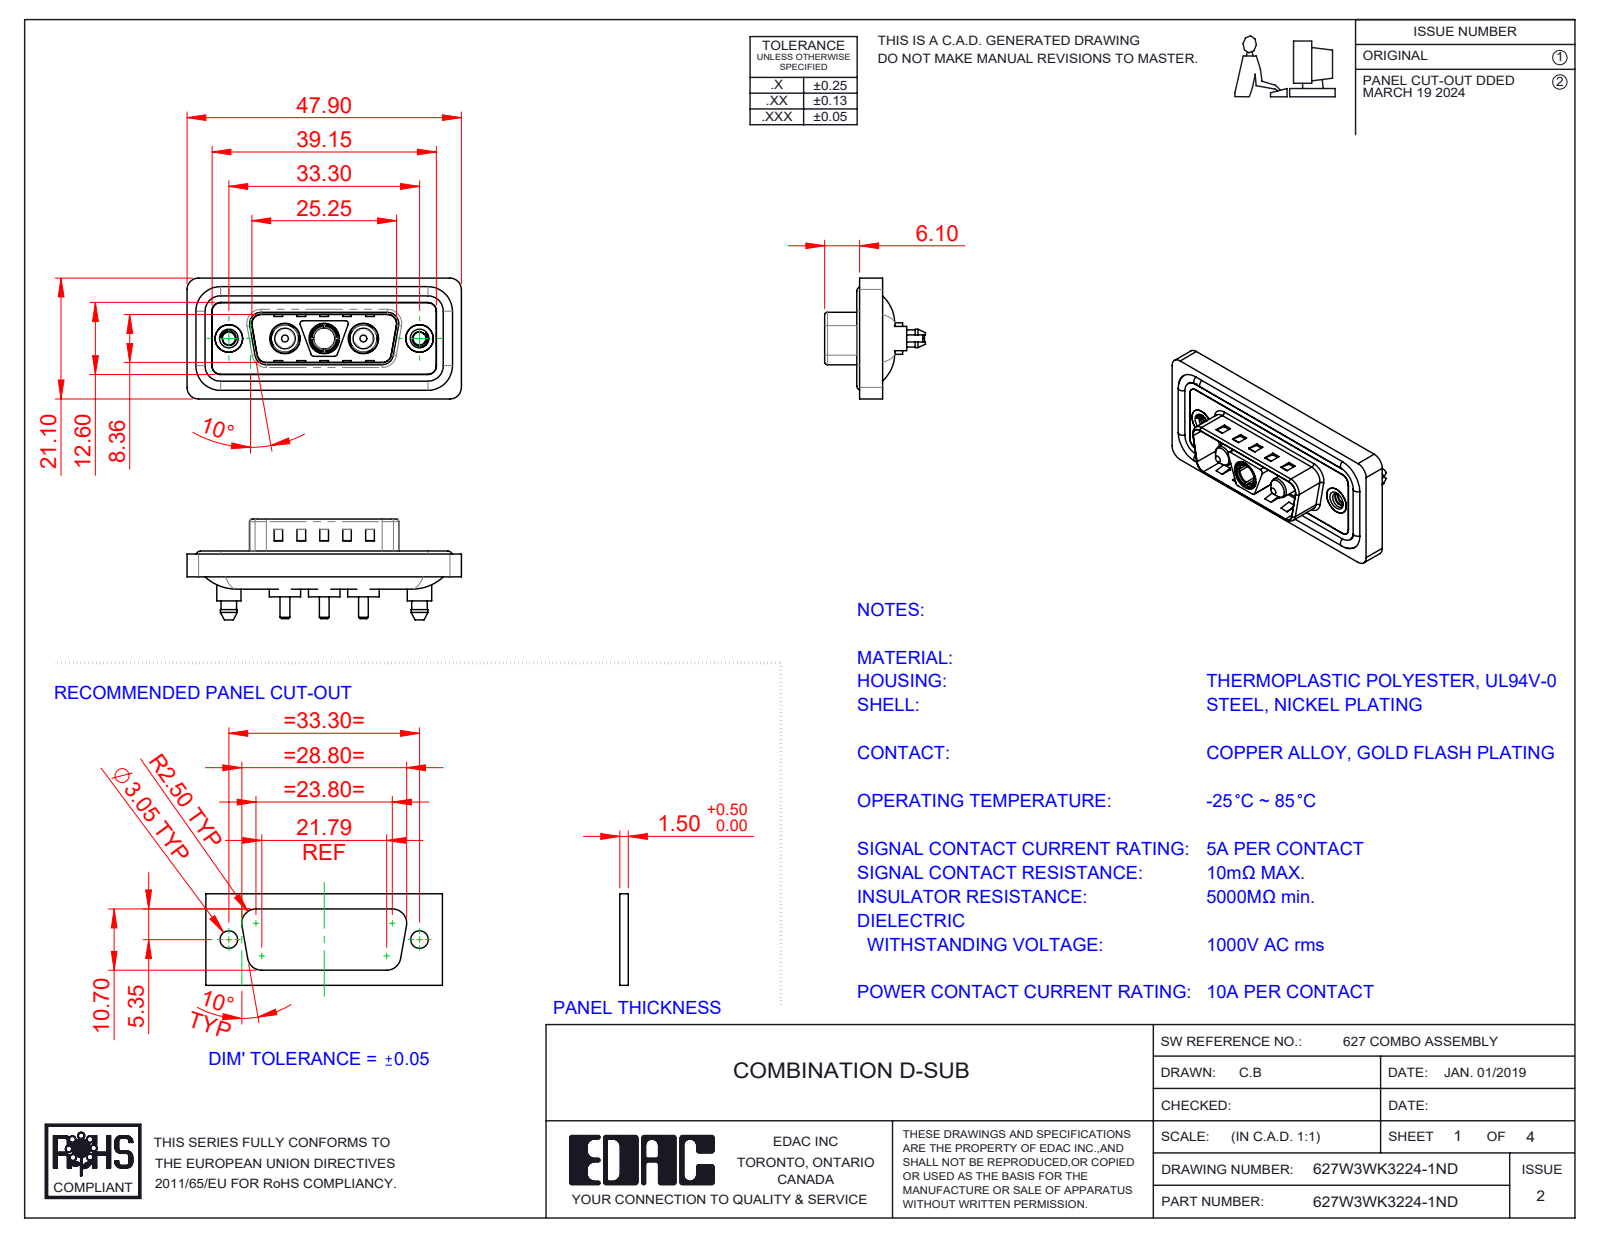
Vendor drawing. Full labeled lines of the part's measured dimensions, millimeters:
Part name (STEP PRODUCT): Power Pin_10A S; 627Combo Housing_3WK3; 627Combo Threaded Boardlock_D; 627W3WK3224-1ND (+5 more)
STEP written by: SolidWorks 2023 (CONFIG_CONTROL_DESIGN)
Units: millimetres
Bodies: 13 solids, 667 faces (247 planar, 290 cylindrical, 130 other)
Overall size (bounding box): 47.9 × 21.1 × 17.6
Volume: 5 779 mm³ · Surface area: 9 425 mm²
Round holes (diameter × count): ⌀4.85 ×3, ⌀5.3 ×3, ⌀2.26 ×2, ⌀4 ×2, ⌀4.8 ×2, ⌀5 ×2, ⌀3.7 ×1
Round bosses / shafts (diameter × count): ⌀1.6 ×4, ⌀5.5 ×3, ⌀5.2 ×3, ⌀4.75 ×3, ⌀3.75 ×3, ⌀1.7 ×3, ⌀5.4 ×2, ⌀4.9 ×2
Partial cylindrical surfaces — rounded edges, fillets, slot ends (radius × count): R1.5 ×28, R2 ×20, R0.5 ×12, R1.6 ×10, R0.25 ×4, R0.6 ×4, R0.65 ×4, R0.9 ×4
Main face-to-face distances: 0.4, 1.5, 1.1, 0.5, 1.6, 3.1, 2.9, 4, 0.7, 0.82
Hole centre spacings: 6.85, 9.8, 16.65, 23.5, 13.7, 33.3
